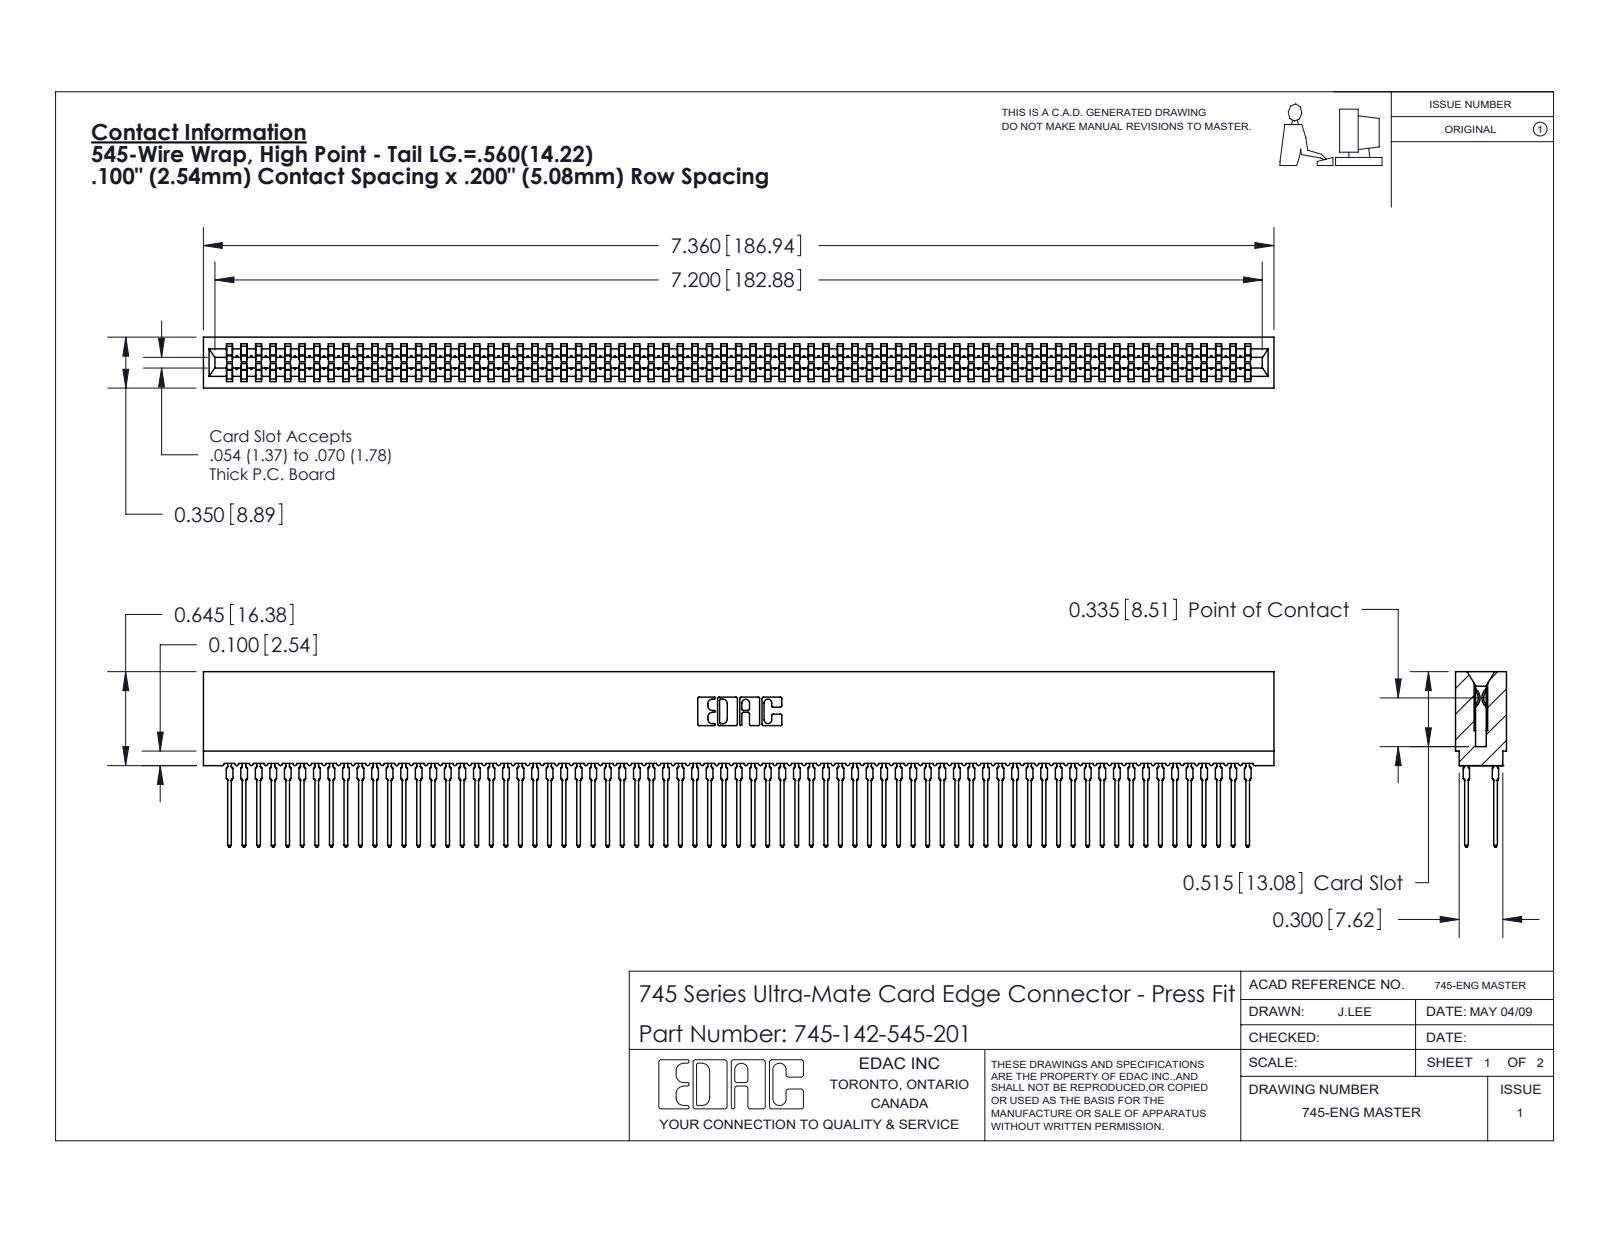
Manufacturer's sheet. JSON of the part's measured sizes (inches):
{"part_name": "745-142-545-201; 745-292-001_545; 745 Part_Insulator Option - 01", "step_written_by": "SolidWorks 2020 (CONFIG_CONTROL_DESIGN)", "units": "inches", "bodies": {"solids": 143, "faces": 12804, "planar": 6587, "cylindrical": 2525, "other": 3692}, "overall_size": [7.36, 1.206, 0.35], "volume_in3": 1.047, "surface_area_in2": 58.47, "partial_cylinders_radius": [[0.021, 284], [0.015, 142], [0.01, 22], [0.005, 8], [0.011, 8], [0.007, 6], [0.031, 6], [0.026, 3]], "face_to_face_distances": [0.063, 0.287, 0.35, 0.045, 0.305, 0.018, 0.243, 0.138, 0.212, 0.093]}
